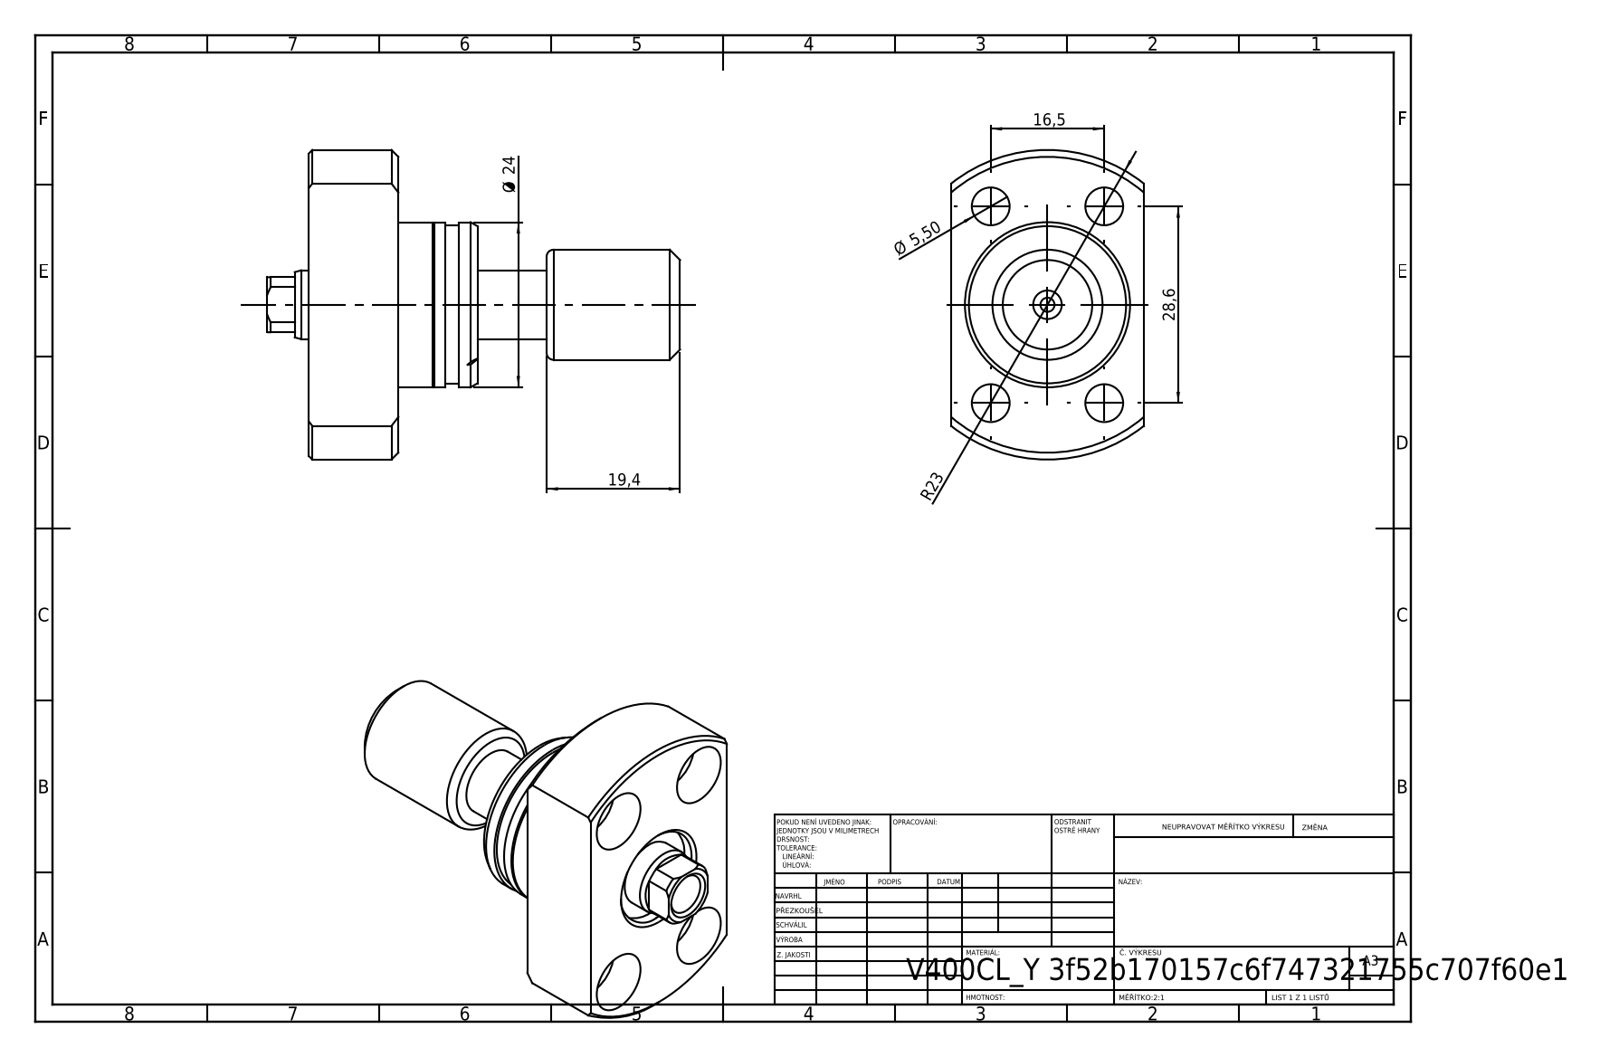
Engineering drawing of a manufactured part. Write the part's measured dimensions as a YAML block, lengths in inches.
part_name: "V400CL_VC_X; V400CL_PC_Y"
step_written_by: "SolidWorks 2019 (CONFIG_CONTROL_DESIGN)"
units: inches
bodies: {solids: 2, faces: 103, planar: 26, cylindrical: 47, other: 30}
overall_size: [2.362, 1.772, 1.102]
volume: 1.37
surface_area: 14.71
round_holes:
  - {diameter: 0.217, count: 4}
  - {diameter: 0.354, count: 4}
  - {diameter: 0.081, count: 1}
  - {diameter: 0.197, count: 1}
  - {diameter: 0.236, count: 1}
  - {diameter: 0.394, count: 1}
  - {diameter: 0.571, count: 1}
round_bosses_or_shafts:
  - {diameter: 0.945, count: 1}
  - {diameter: 0.906, count: 1}
  - {diameter: 0.63, count: 1}
partial_cylinders:
  - {radius: 0.187, count: 1}
  - {radius: 0.886, count: 1}
face_to_face_distances: [0.512, 1.102, 0.453, 0.965, 0.748, 0.295, 0.217, 0.079, 0.138, 1.159]
hole_center_spacings: [0.65, 0.65, 1.126, 1.3]
